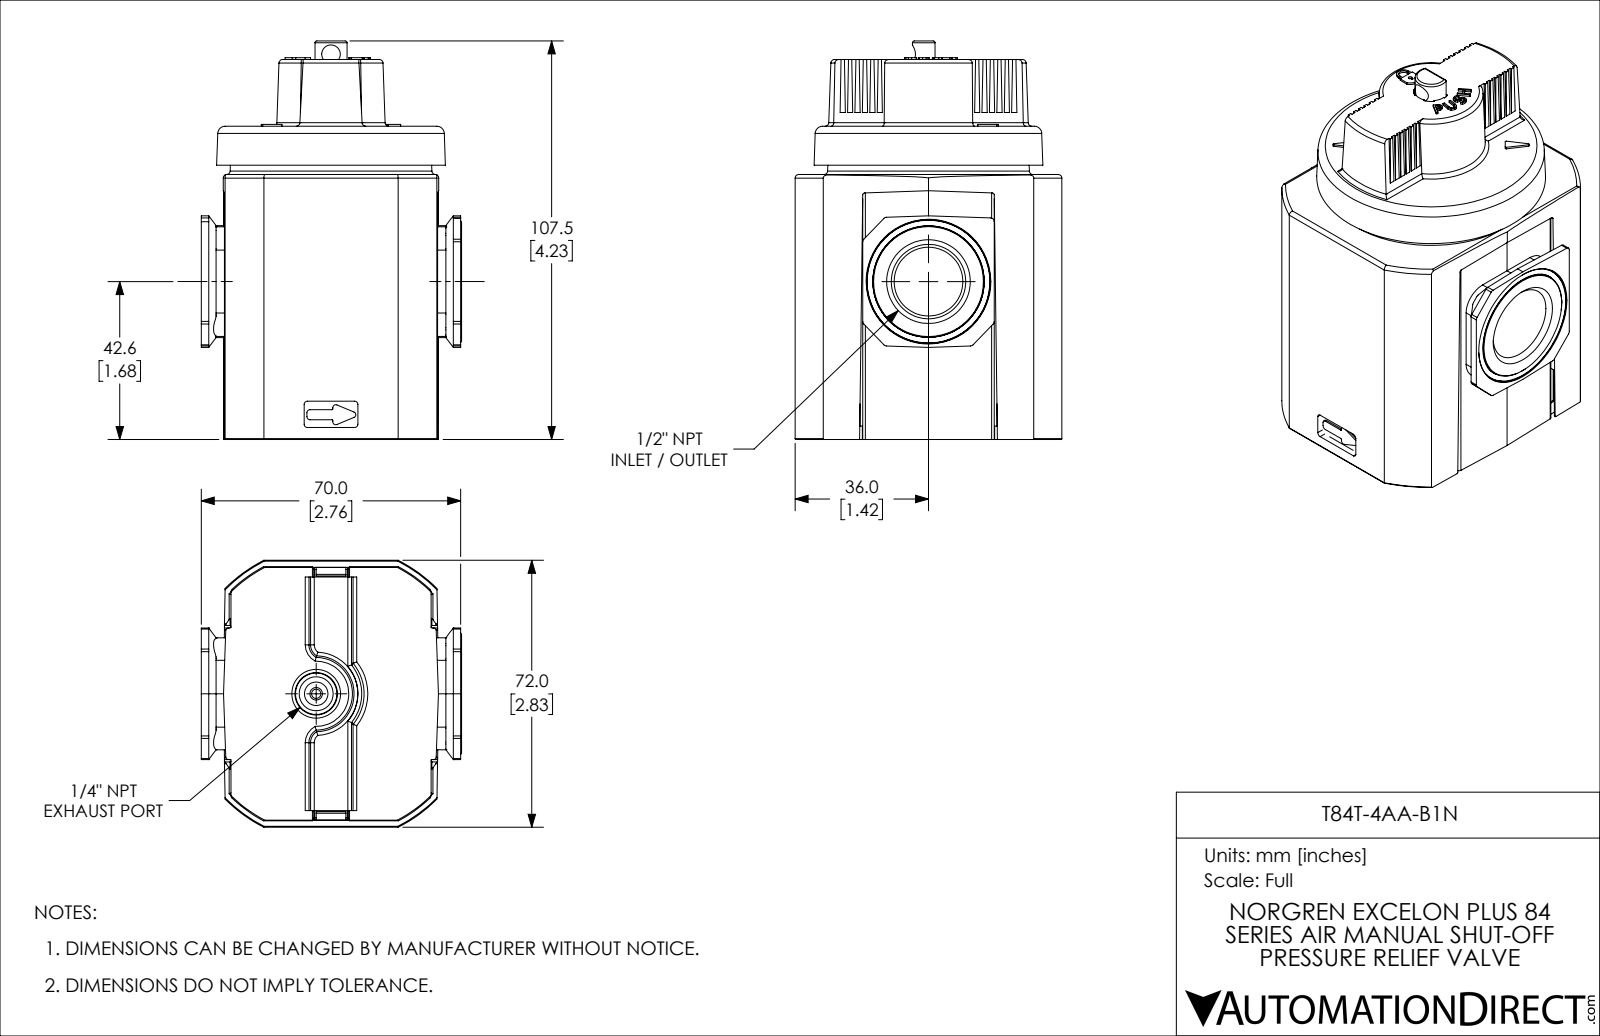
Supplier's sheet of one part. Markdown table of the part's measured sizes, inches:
| quantity | value |
| --- | --- |
| part name | T84T-4AA-B1N |
| STEP written by | SolidWorks 2021 (CONFIG_CONTROL_DESIGN) |
| units | inches |
| bodies | 3 solids, 712 faces (365 planar, 227 cylindrical, 120 other) |
| overall size | 4.232 × 2.835 × 2.766 |
| volume | 12.15 in³ |
| surface area | 123.5 in² |
| round holes (diameter × count) | 0.039 × 1, 0.197 × 1, 0.451 × 1, 1.551 × 1 |
| round bosses / shafts (diameter × count) | 0.984 × 1, 0.669 × 1 |
| partial cylindrical surfaces (radius × count) | 0.039 × 30, 0.03 × 16, 0.01 × 15, 0.02 × 9, 0.035 × 4, 0.079 × 4, 0.157 × 4, 0.248 × 4 |
| main face-to-face distances | 2.913, 2.835, 2.756, 0.157, 0.413, 0.144, 2.77, 2.281, 0.512, 0.571 |
| hole center spacings | 0.157, 0.315 |
